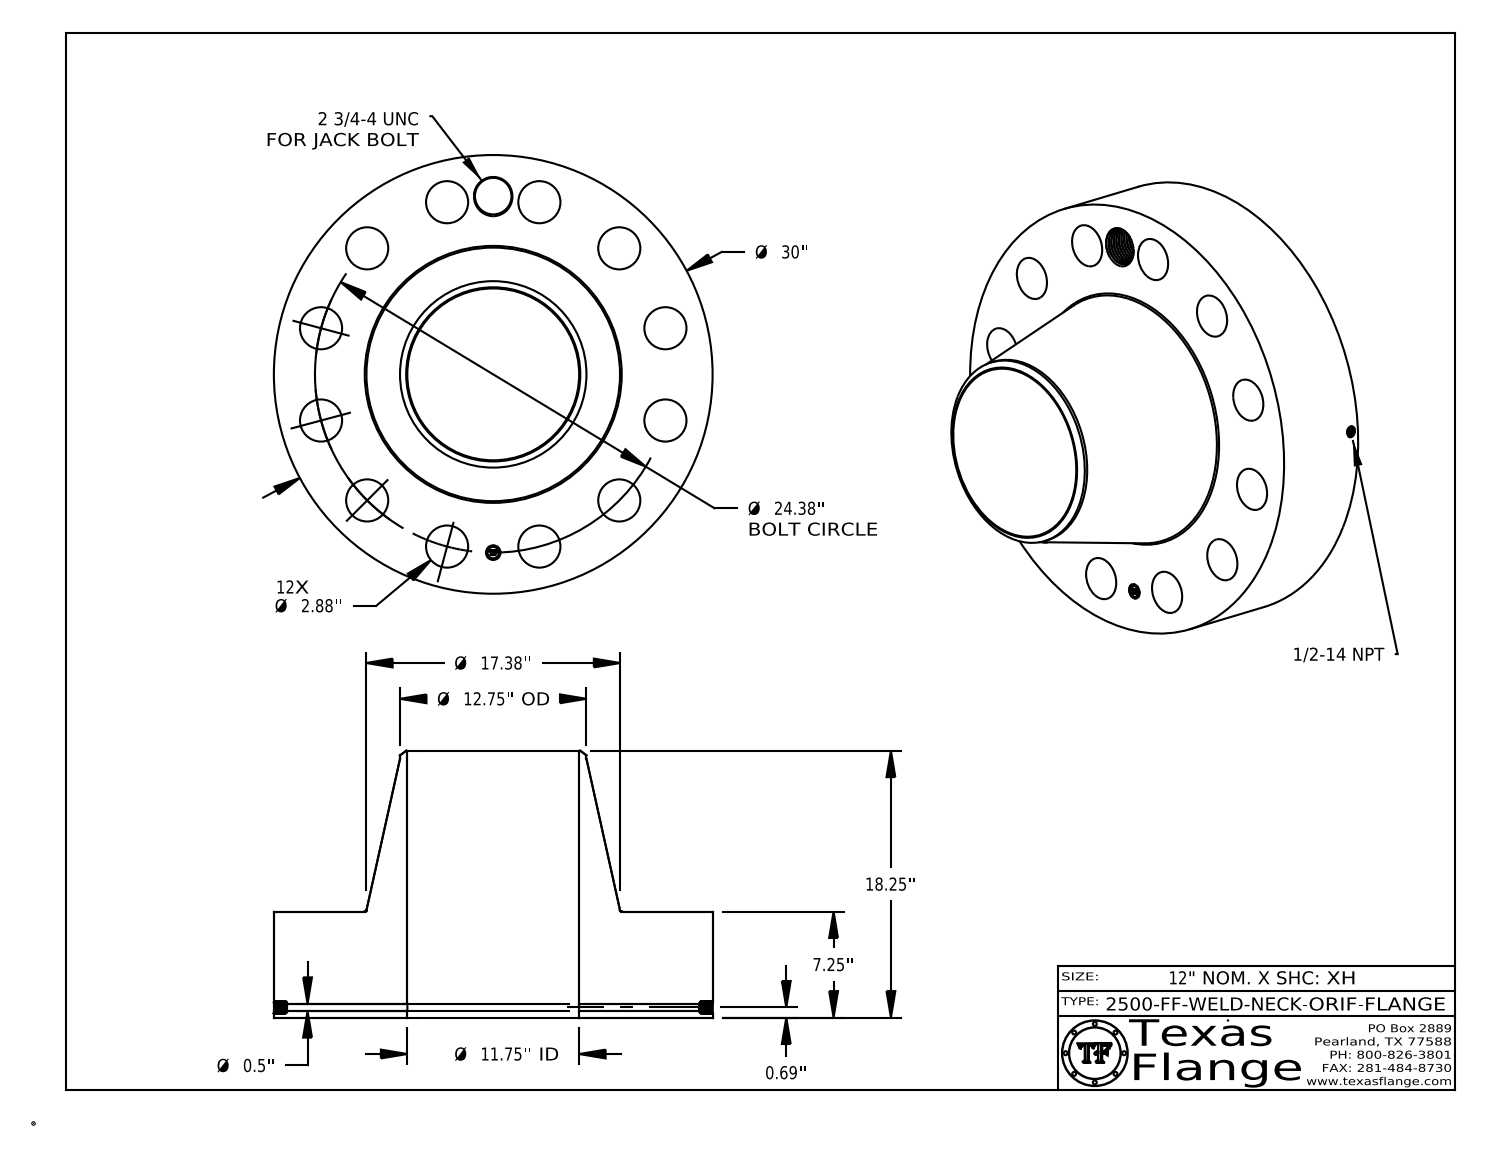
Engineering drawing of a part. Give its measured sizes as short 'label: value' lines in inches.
name: 2500-FF-WELD-NECK
written by: CATIA V5 STEP AP214 (AUTOMOTIVE_DESIGN)
unit: in
bodies: 1 solid, 858 faces (368 planar, 128 cylindrical, 362 other)
size: 30 × 30 × 18.25
volume: 4 480 in³; area: 3 699 in²
holes: 12× ⌀2.88, 1× ⌀0.5, 1× ⌀0.672, 1× ⌀1, 1× ⌀2.5, 1× ⌀11.75
bosses: 8× ⌀0.061, 1× ⌀30, 1× ⌀12.75, 1× ⌀0.788
face distances: 7.25, 18.25, 11, 0.015, 7.235, 11.015, 0.298, 0.292, 0.054, 0.248
hole spacings: 12.19, 17.239, 23.55, 6.31, 21.114, 24.38, 3.182, 6.31
